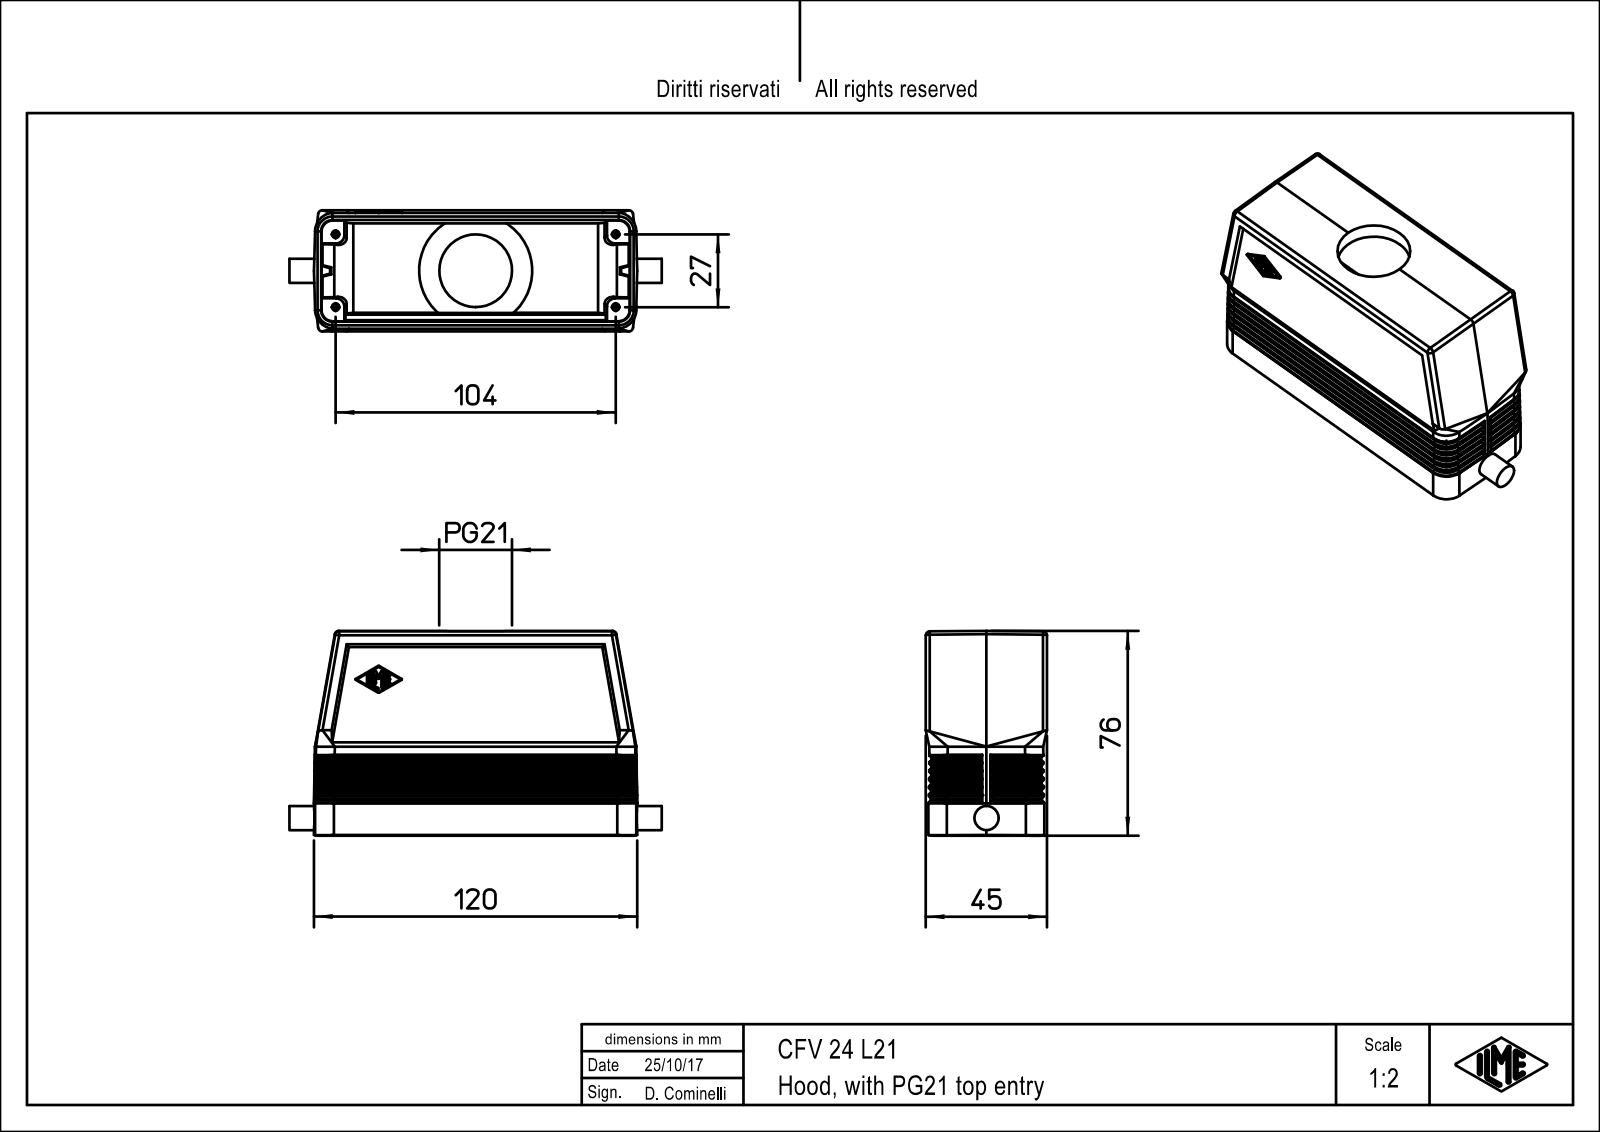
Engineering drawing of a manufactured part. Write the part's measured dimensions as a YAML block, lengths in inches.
part_name: "CFV_24_L21"
step_written_by: "PTC Creo Elements/Direct Modeling 19.0E 27-Jun-2016 (C) Parametric Technology GmbH (AUTOMOTIVE_DESIGN)"
units: inches
bodies: {solids: 1, faces: 511, planar: 236, cylindrical: 139, other: 136}
overall_size: [5.441, 2.992, 1.772]
volume: 6.616
surface_area: 84.39
round_holes:
  - {diameter: 1.063, count: 1}
round_bosses_or_shafts:
  - {diameter: 0.354, count: 1}
partial_cylinders:
  - {radius: 0.02, count: 78}
  - {radius: 0.013, count: 15}
  - {radius: 0.059, count: 10}
  - {radius: 0.276, count: 8}
  - {radius: 0.118, count: 4}
  - {radius: 0.165, count: 4}
  - {radius: 0.007, count: 3}
  - {radius: 0.026, count: 1}
face_to_face_distances: [1.693, 0.079, 0.079, 0.157, 0.039, 1.732, 0.333, 0.236, 0.237, 0.158]
